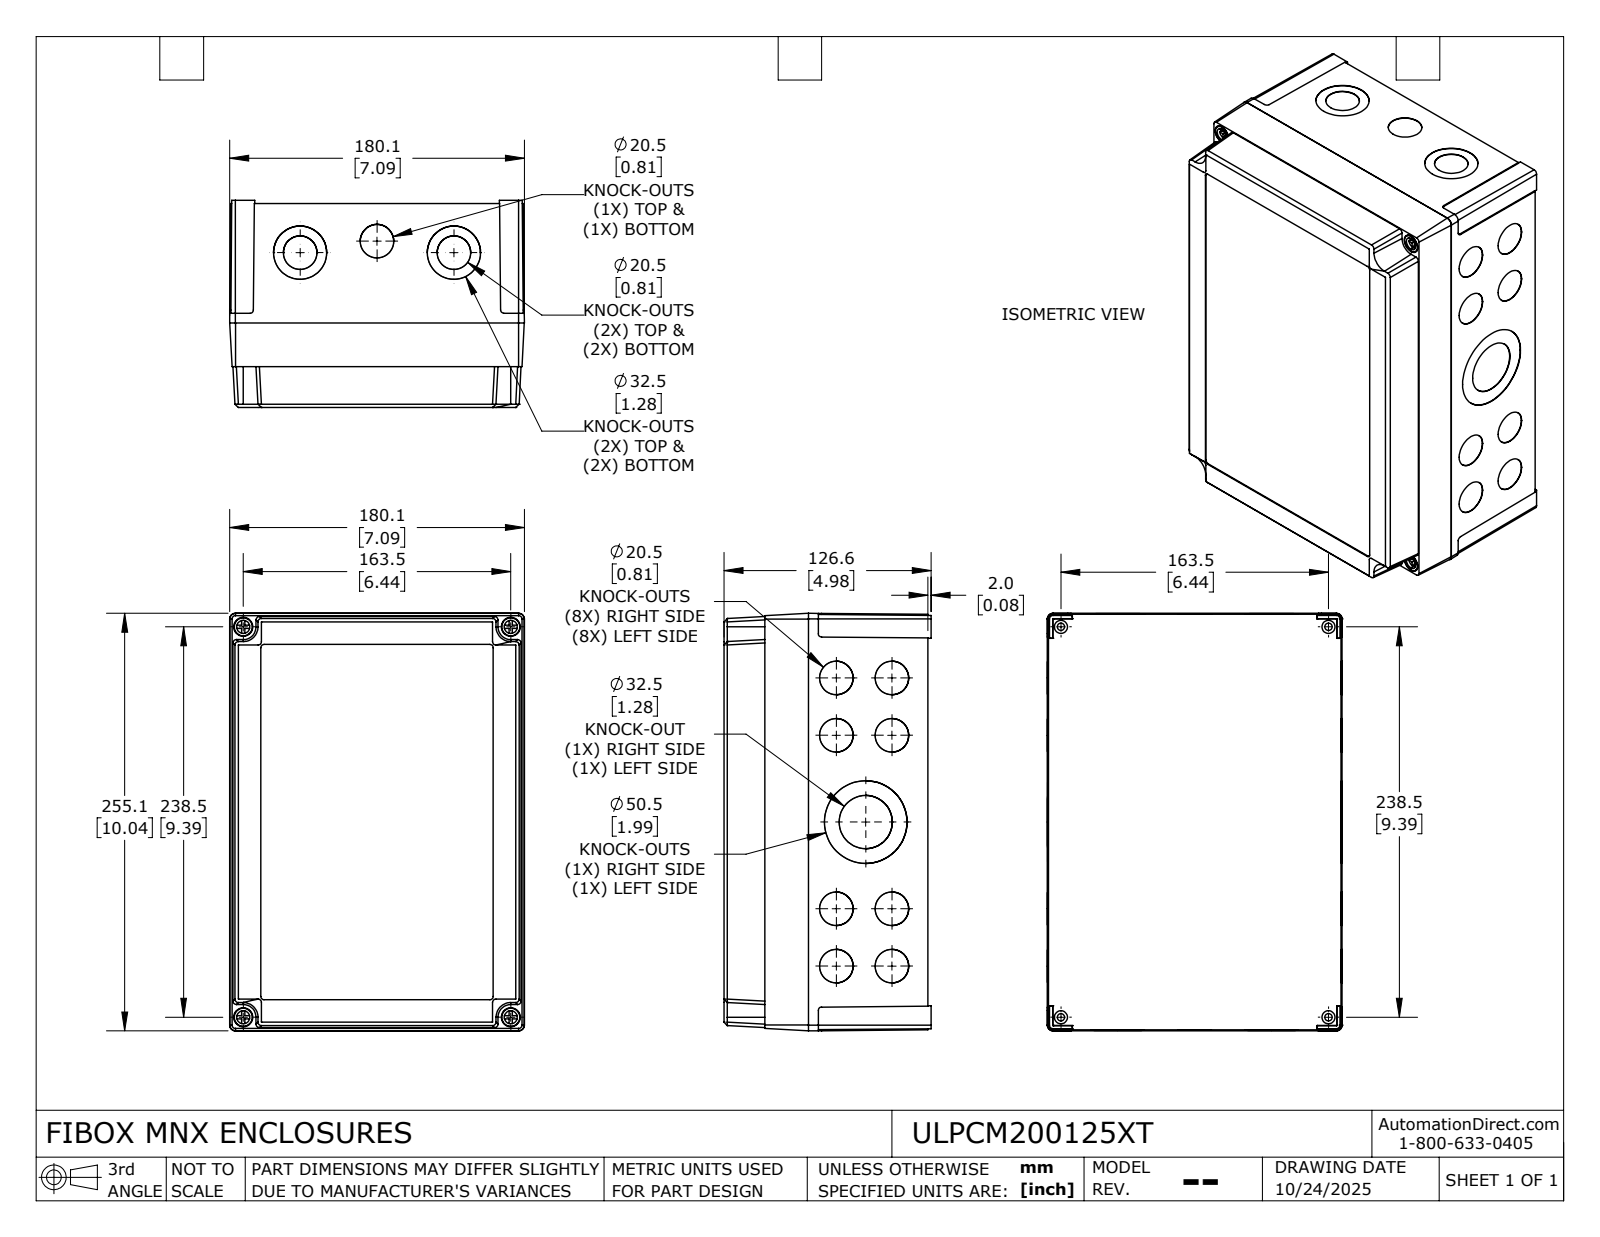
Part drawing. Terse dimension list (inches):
name: ULPCM200125XT_Default
written by: SolidWorks 2024 (CONFIG_CONTROL_DESIGN)
unit: in
bodies: 6 solids, 767 faces (425 planar, 292 cylindrical, 50 other)
size: 10.043 × 7.091 × 4.984
volume: 37.21 in³; area: 628 in²
holes: 22× ⌀0.807, 20× ⌀0.126, 20× ⌀0.157, 6× ⌀1.28, 4× ⌀0.177, 4× ⌀0.315, 4× ⌀0.457, 2× ⌀1.988
bosses: 16× ⌀0.315, 8× ⌀0.098, 4× ⌀0.433, 4× ⌀0.283, 4× ⌀0.276
rounds: 8× R0.079, 8× R0.083, 6× R0.112, 4× R0.042, 4× R0.197, 2× R0.046
face distances: 0.165, 4.803, 0.118, 4.685, 4.886, 4.768, 0.083, 0.077, 0.055, 0.022
hole spacings: 1.378, 1.339, 1.921, 1.939, 5.046, 5.551, 5.71, 4.921
